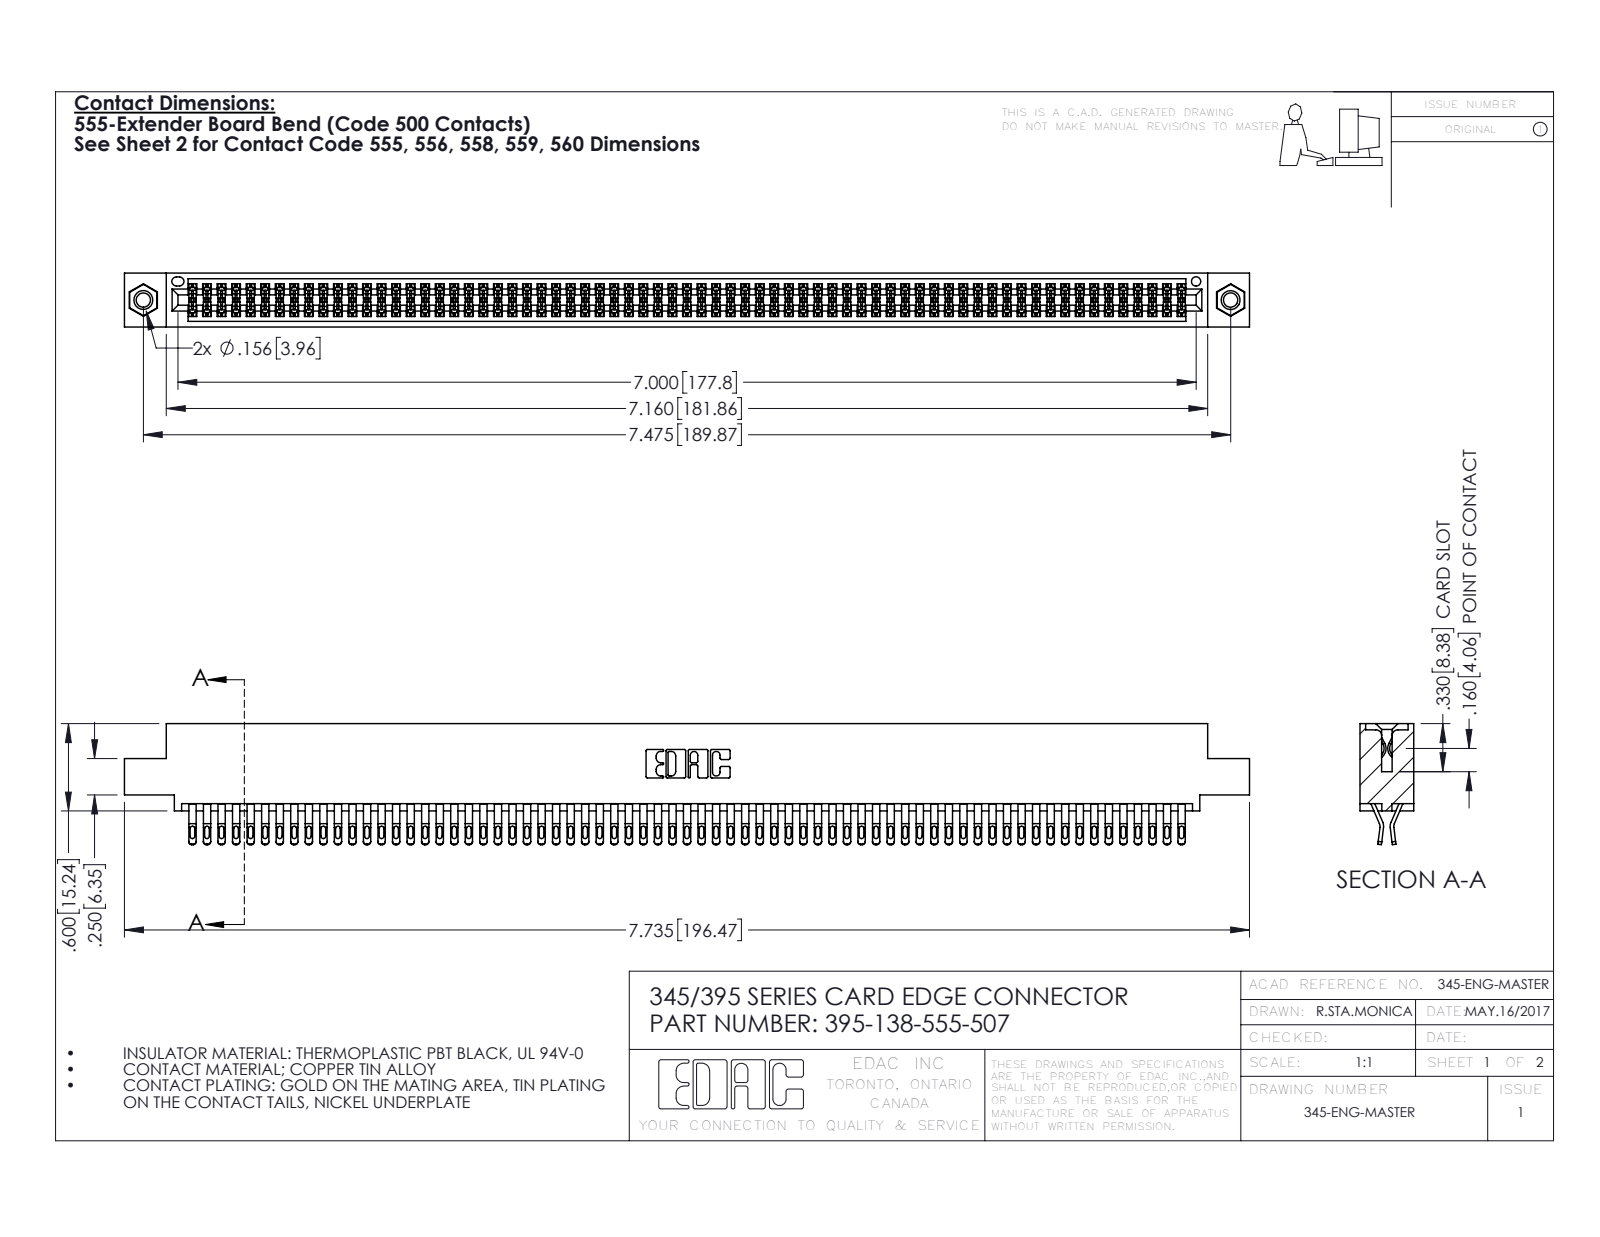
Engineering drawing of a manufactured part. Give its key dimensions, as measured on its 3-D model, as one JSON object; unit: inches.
{"part_name": "345-250-001_345-250-005-103; 345-292-001_555 Tail; 345 Part_0.110 Offset - 0.156 Dia-TI; 395-138-555-507", "step_written_by": "SolidWorks 2016 (CONFIG_CONTROL_DESIGN)", "units": "inches", "bodies": {"solids": 141, "faces": 7918, "planar": 4394, "cylindrical": 3508, "other": 16}, "overall_size": [7.735, 0.832, 0.37], "volume_in3": 1.199, "surface_area_in2": 48.18, "round_holes": [[0.098, 2], [0.125, 2], [0.156, 2], [0.064, 1]], "round_bosses_or_shafts": [[0.155, 2]], "partial_cylinders_radius": [[0.016, 345], [0.02, 276], [0.006, 207], [0.01, 22], [0.007, 6], [0.031, 6], [0.026, 3], [0.01, 2]], "face_to_face_distances": [0.072, 0.298, 0.025, 0.37, 0.2, 0.098, 0.272, 0.225, 0.175, 0.149], "hole_center_spacings": [0.27, 7.239, 7.475]}
